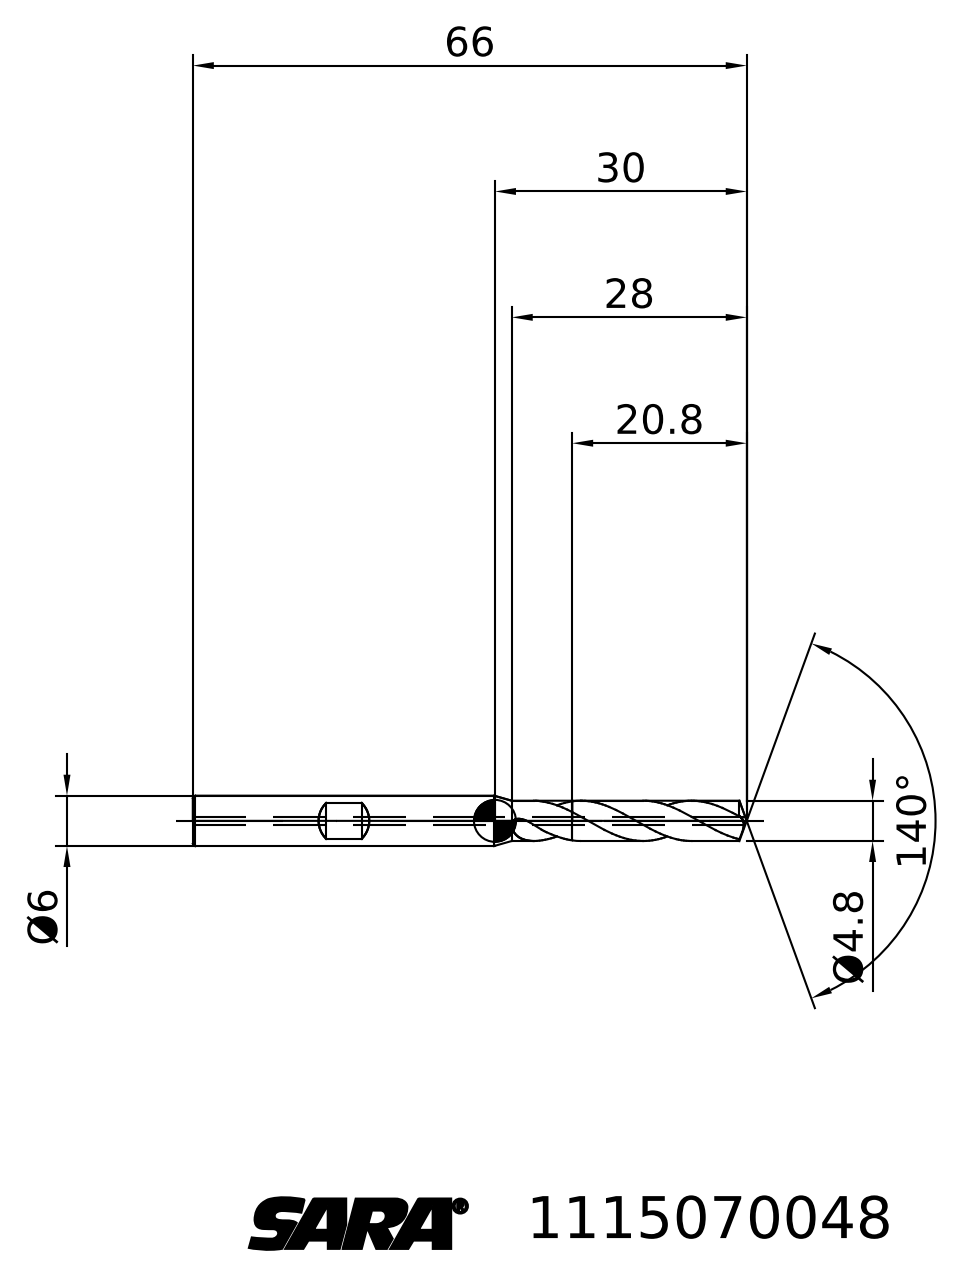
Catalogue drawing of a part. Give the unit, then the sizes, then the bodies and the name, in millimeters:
Units: millimetres
Overall size (bounding box): 66 × 6 × 6
Main face-to-face distances: 45.2
Volume: 1 384 mm³ · Surface area: 1 223 mm²
Bodies: 2 solids, 29 faces (6 planar, 0 cylindrical, 23 other)
STEP written by: TDM (AUTOMOTIVE_DESIGN)
